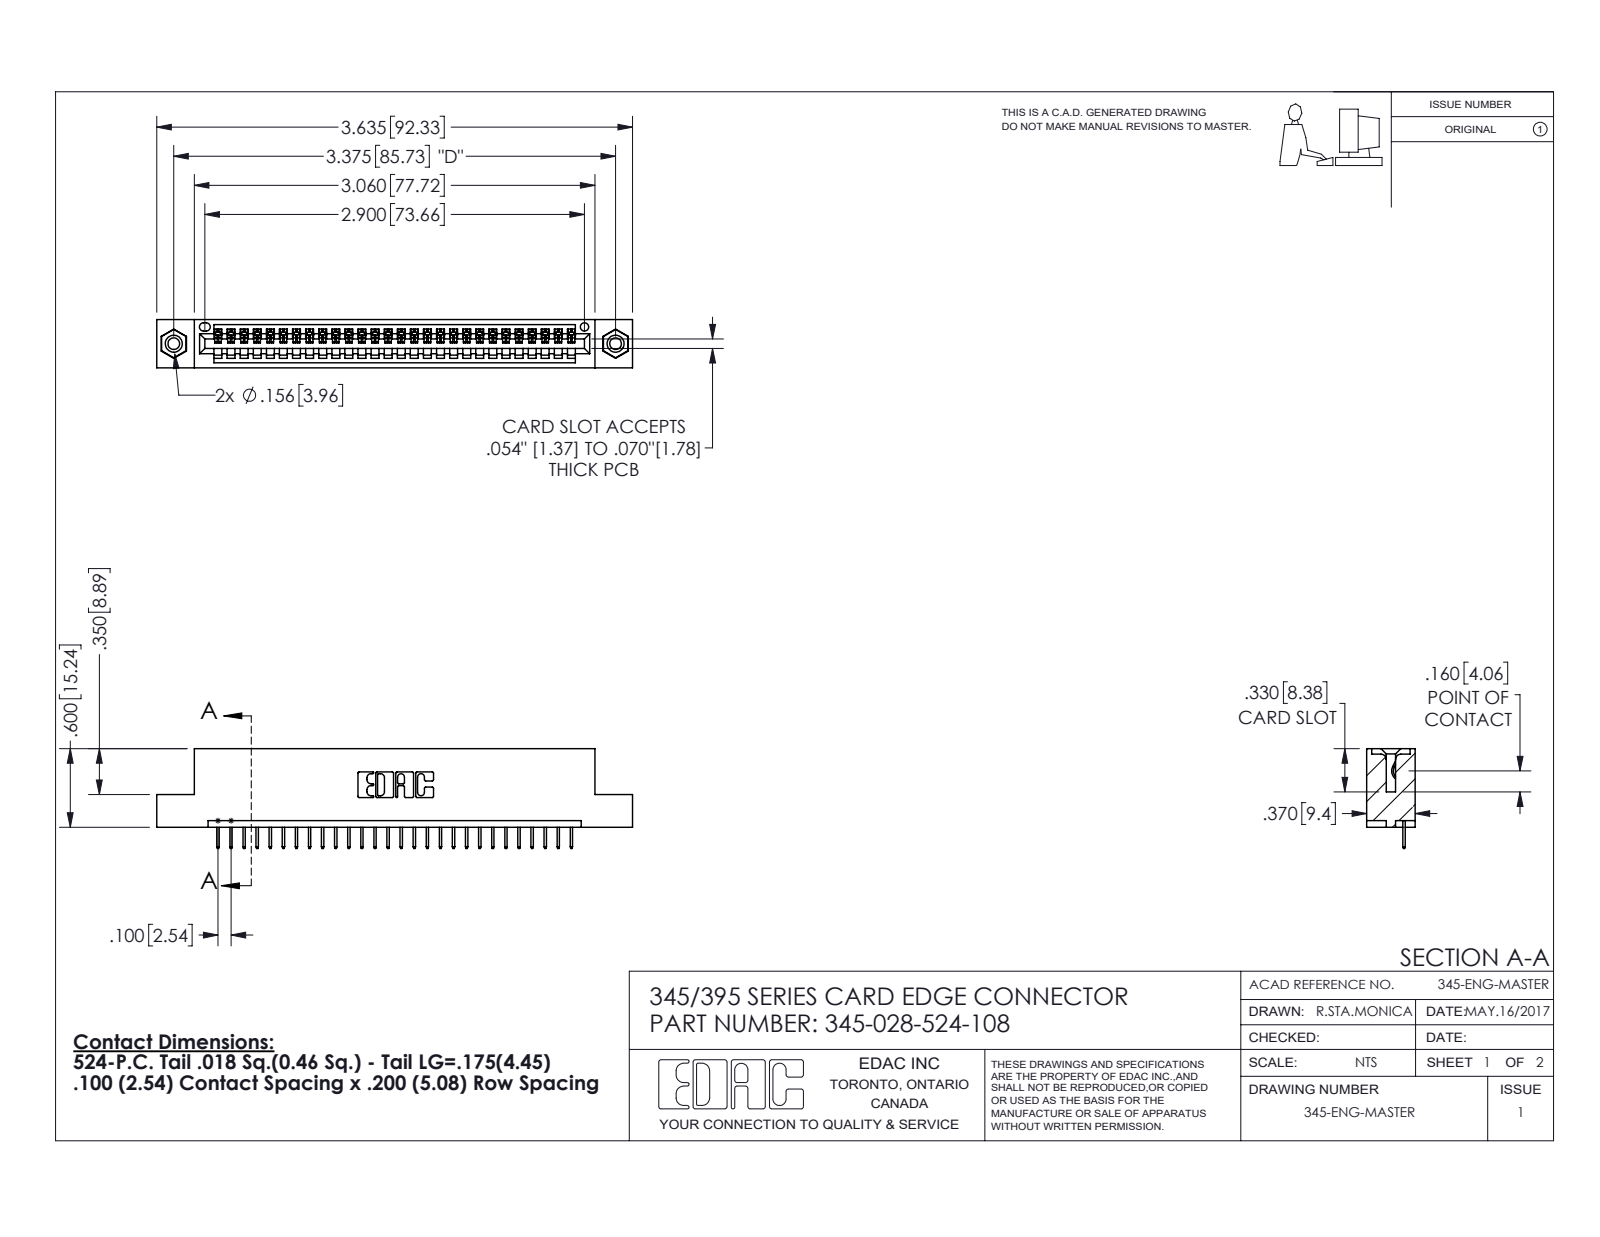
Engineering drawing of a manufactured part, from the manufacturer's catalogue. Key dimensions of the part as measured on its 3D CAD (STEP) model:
Part name (STEP PRODUCT): 345-250-001_345-250-003-102; 345 Part_Flush Mounting Lugs - 0.156 Dia-TI; 345-028-524-108; 345-292-001_345-293-124
STEP written by: SolidWorks 2016 (CONFIG_CONTROL_DESIGN)
Units: inches
Bodies: 31 solids, 1922 faces (1400 planar, 506 cylindrical, 16 other)
Overall size (bounding box): 3.635 × 0.762 × 0.37
Volume: 0.521 in³ · Surface area: 16.77 in²
Round holes (diameter × count): ⌀0.089 ×2, ⌀0.125 ×2, ⌀0.156 ×2, ⌀0.064 ×1
Round bosses / shafts (diameter × count): ⌀0.155 ×2
Partial cylindrical surfaces — rounded edges, fillets, slot ends (radius × count): R0.006 ×56, R0.01 ×22, R0.007 ×6, R0.031 ×6, R0.026 ×3, R0.031 ×2, R0.04 ×2, R0.014 ×1
Main face-to-face distances: 0.072, 0.298, 0.37, 0.2, 0.098, 0.272, 0.025, 0.225, 0.072, 0.149
Hole centre spacings: 0.27, 3.14, 3.375
